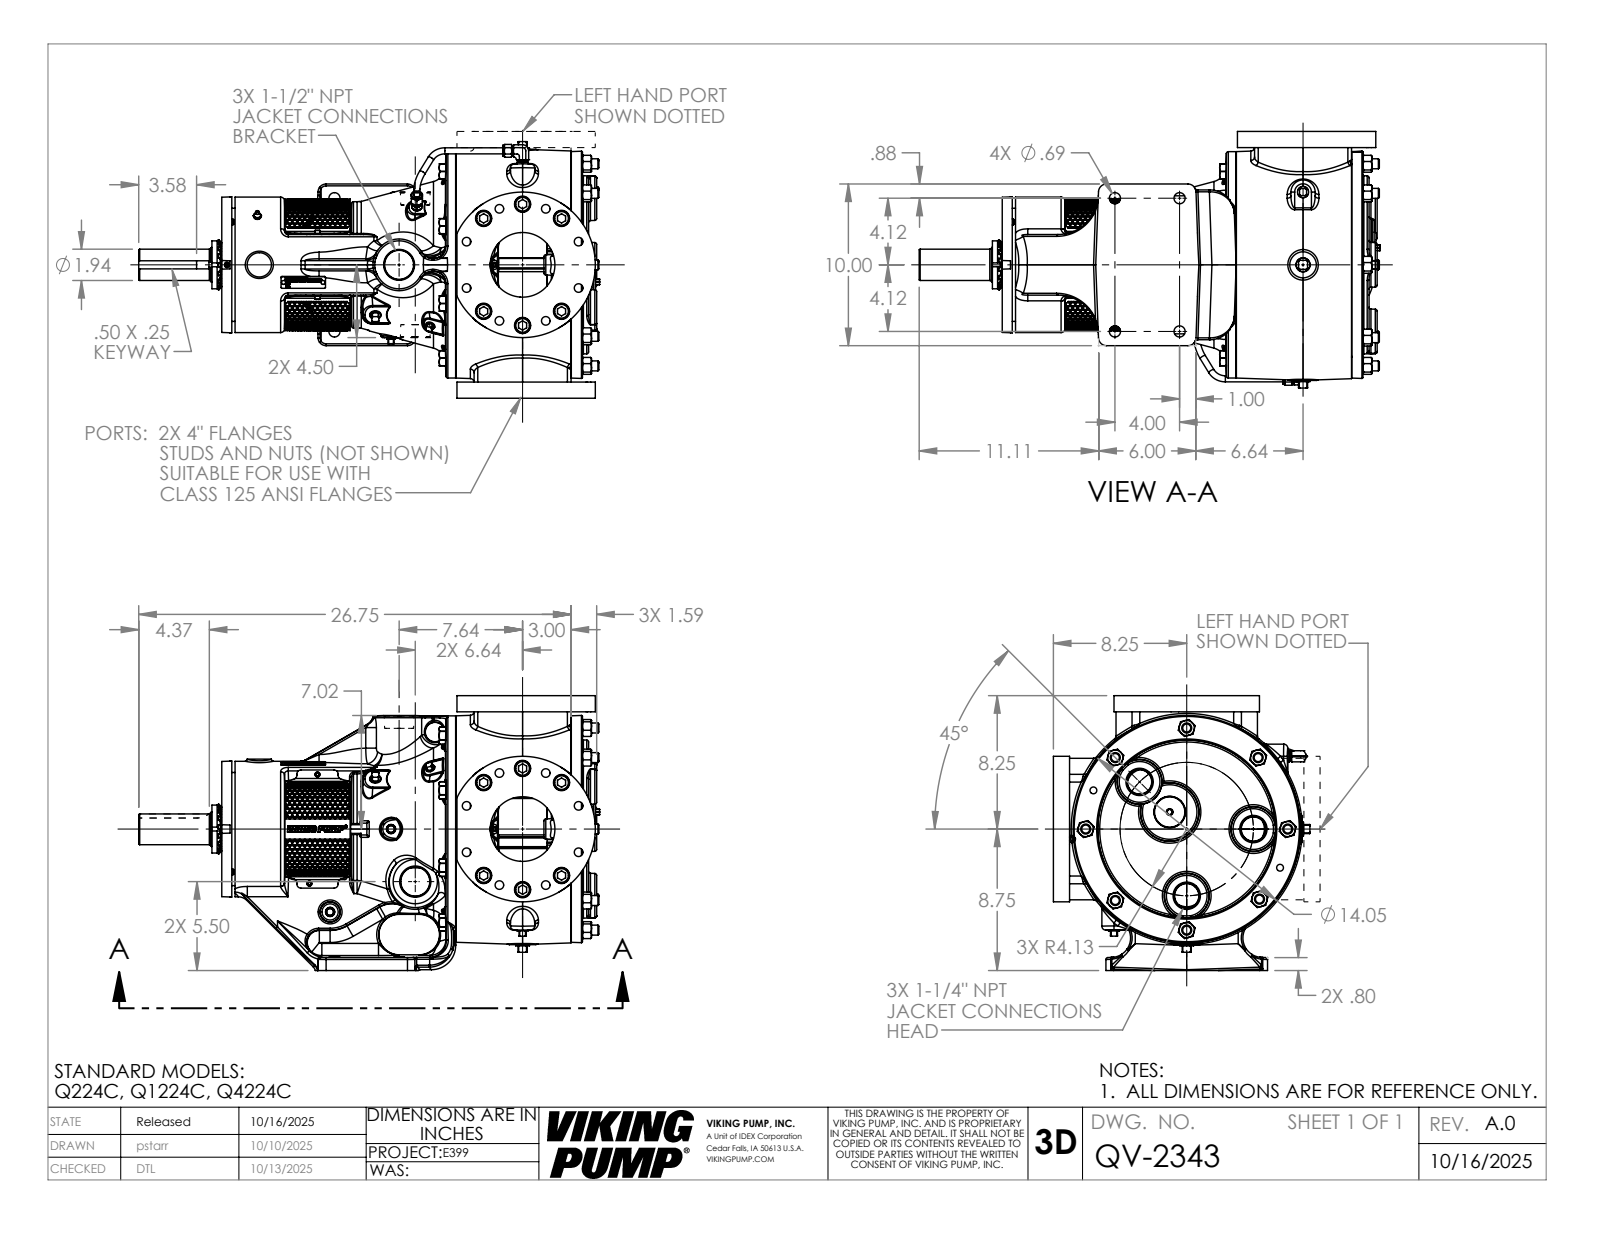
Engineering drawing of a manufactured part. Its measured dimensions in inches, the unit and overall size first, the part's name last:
Units: inches
Overall size (bounding box): 28.514 × 17 × 15.971
Round holes (diameter × count): ⌀0.531 ×16, ⌀0.656 ×12, ⌀1 ×12, ⌀0.25 ×9, ⌀0.266 ×8, ⌀1.157 ×8, ⌀0.688 ×4, ⌀0.159 ×2, ⌀0.313 ×2, ⌀0.422 ×2, ⌀4 ×2, ⌀0.453 ×1
Round bosses / shafts (diameter × count): ⌀0.937 ×12, ⌀0.625 ×9, ⌀0.617 ×8, ⌀0.375 ×4, ⌀0.625 ×3, ⌀0.312 ×3, ⌀0.19 ×3, ⌀9 ×2
Partial cylindrical surfaces — rounded edges, fillets, slot ends (radius × count): R0.12 ×54, R0.75 ×24, R0.015 ×18, R0.092 ×18, R0.07 ×16, R0.5 ×12, R0.24 ×10, R0.25 ×10
Main face-to-face distances: 0.38, 17, 22.317, 22.698, 3.82, 18.498, 18.878, 1, 7.972, 4.153
Hole centre spacings: 3.75, 5.303, 2.87, 6.929, 2.079, 5.783, 7.5, 1.463
Volume: 2 371 in³ · Surface area: 2 075 in²
Bodies: 1 solid, 4030 faces (1388 planar, 702 cylindrical, 1940 other)
Part name (STEP PRODUCT): QV-2343
STEP written by: SolidWorks 2024 (AUTOMOTIVE_DESIGN)
